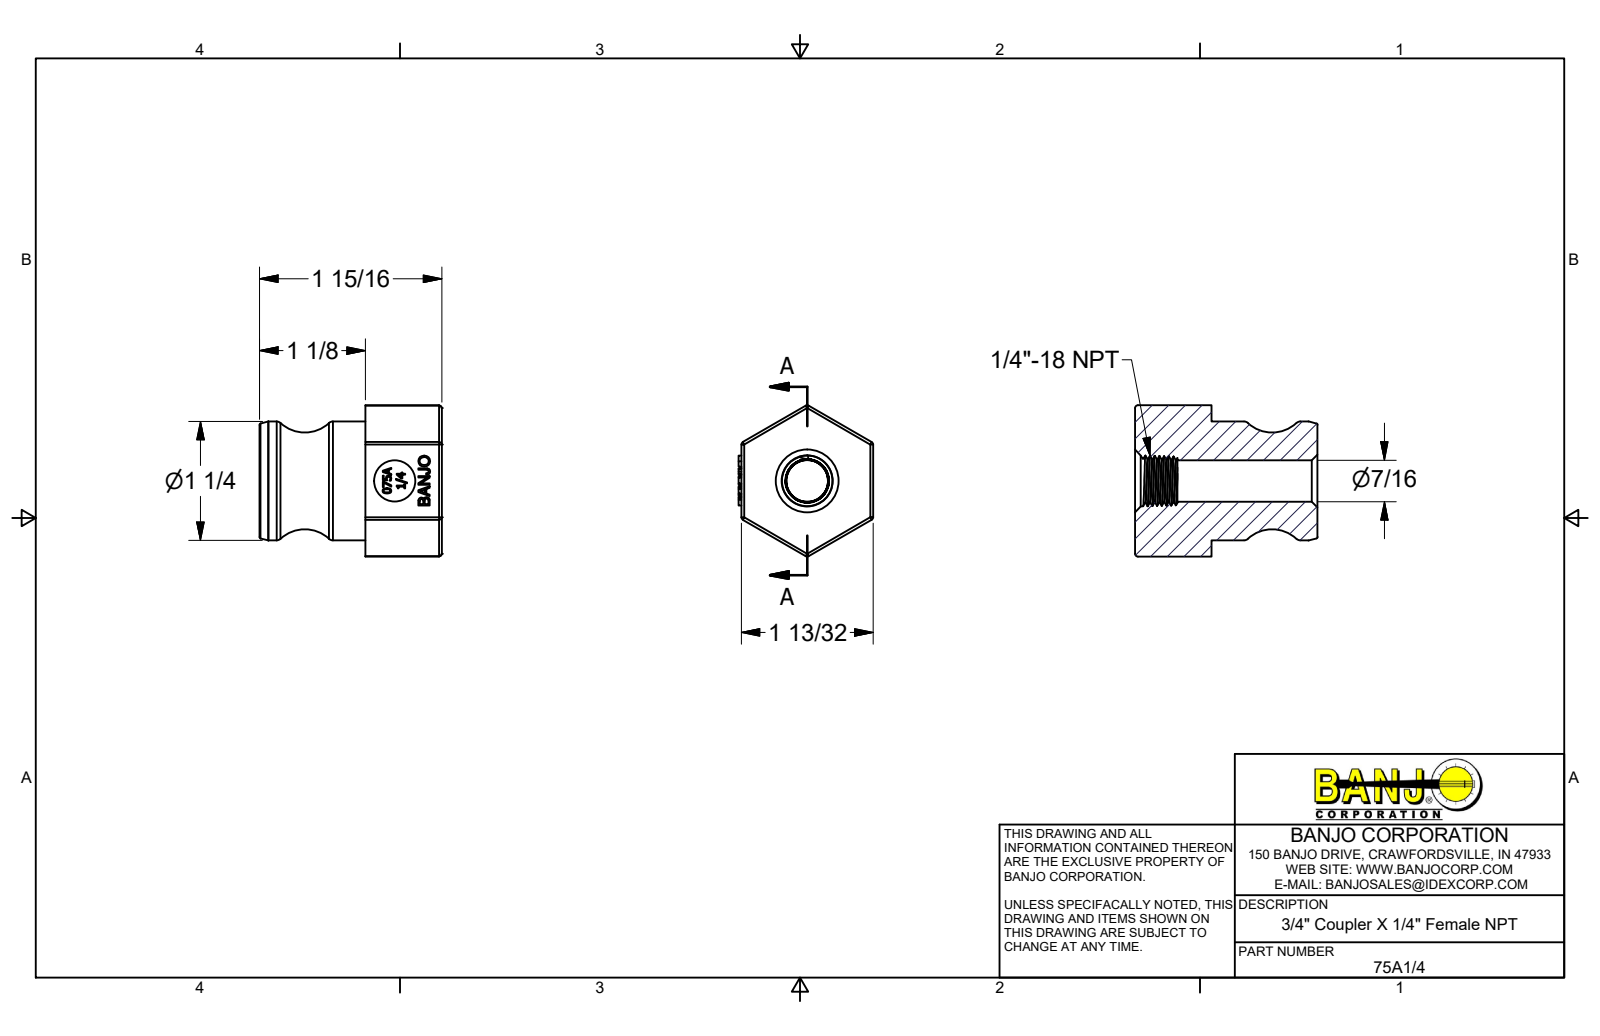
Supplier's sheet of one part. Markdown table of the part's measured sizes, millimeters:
| quantity | value |
| --- | --- |
| part name | 75A025; 75A025U |
| STEP written by | Autodesk Inventor 2017 (AUTOMOTIVE_DESIGN) |
| units | millimeters |
| bodies | 1 solid, 213 faces (119 planar, 18 cylindrical, 76 other) |
| overall size | 49.21 × 40.82 × 36.32 |
| volume | 37 698 mm³ |
| surface area | 9 367 mm² |
| round holes (diameter × count) | 11.11 × 1, 11.18 × 1 |
| round bosses / shafts (diameter × count) | 32.11 × 1 |
| partial cylindrical surfaces (radius × count) | 0.76 × 6, 0.79 × 6, 4.37 × 1 |
| main face-to-face distances | 35.56, 49.21, 28.58, 20.63, 35.3, 37.78, 9.2, 11.43, 0.76, 36.32 |
